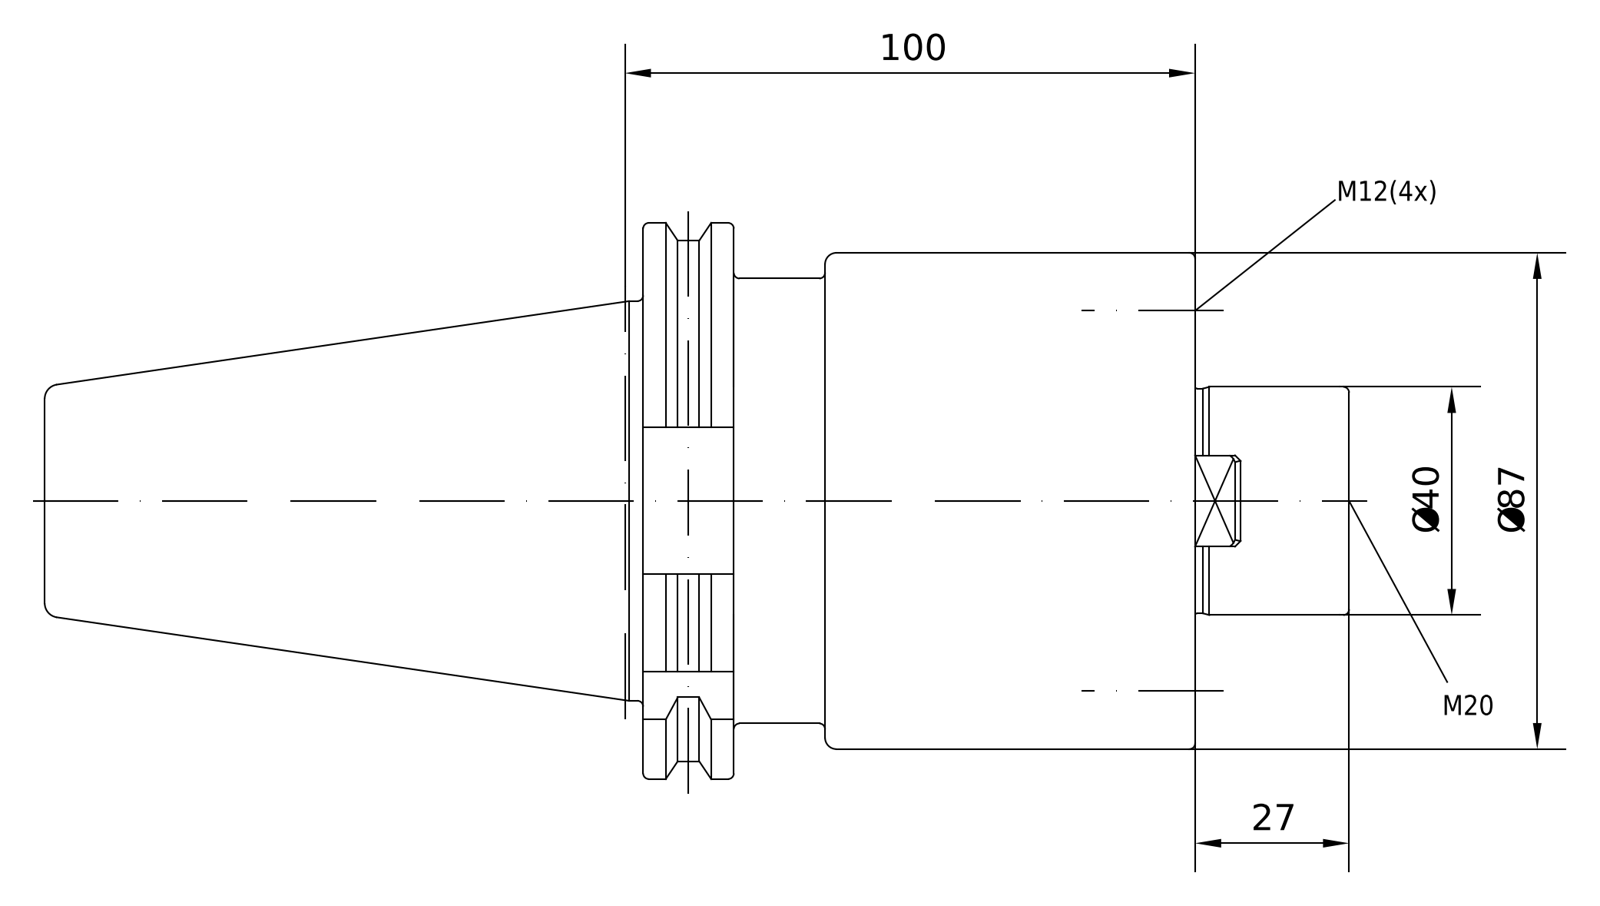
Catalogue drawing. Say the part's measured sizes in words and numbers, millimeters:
The part is named "50-351-40". Its 3-D file was written by "PRO/ENGINEER BY PARAMETRIC TECHNOLOGY CORPORATION, 2010430 (CONFIG_CONTROL_DESIGN)". It is 1 solid with 150 faces: 40 planar, 47 cylindrical and 63 other. Overall it measures 228.6 by 97.47 by 94 millimeters. Its volume is 836 413 cubic millimeters and its surface area 83 017 square millimeters. Round holes: 4 of diameter 10.2, 4 of diameter 12, 1 of diameter 17.5, 1 of diameter 20, 1 of diameter 20.75, 1 of diameter 25.01, 1 of diameter 25.7. Round bosses or shafts: 1 of diameter 91, 1 of diameter 89, 1 of diameter 69.15, 1 of diameter 40, 1 of diameter 24.01. Partial cylindrical surfaces (rounded edges, fillets, slot ends): 1 of radius 1.75, 1 of radius 39, 1 of radius 48.74. The main face-to-face distances are 96.8, 15.85, 80.95, 16, 31.85, 64.95, 123.8, 107.95, 91.95, 27. The hole center spacings are 33.35, 47.16, 66.69.
